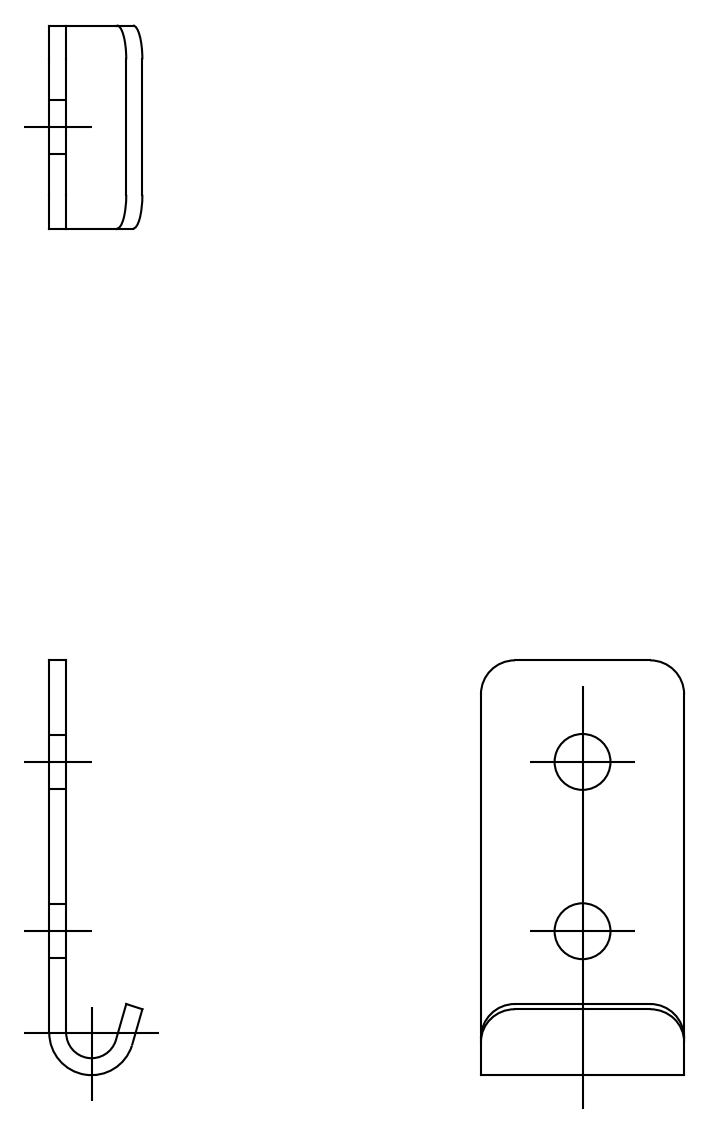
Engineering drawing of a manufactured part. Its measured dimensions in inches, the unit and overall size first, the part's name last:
Units: inches
Overall size (bounding box): 0.984 × 0.472 × 0.217
Round holes (diameter × count): ⌀0.13 ×2
Partial cylindrical surfaces — rounded edges, fillets, slot ends (radius × count): R0.079 ×4, R0.059 ×1, R0.098 ×1
Main face-to-face distances: 0.039, 0.472
Hole centre spacings: 0.394
Volume: 0.021 in³ · Surface area: 1.22 in²
Bodies: 1 solid, 18 faces (8 planar, 10 cylindrical, 0 other)
STEP written by: spGate 20.6.3 (****-****-****-****) (AUTOMOTIVE_DESIGN)
